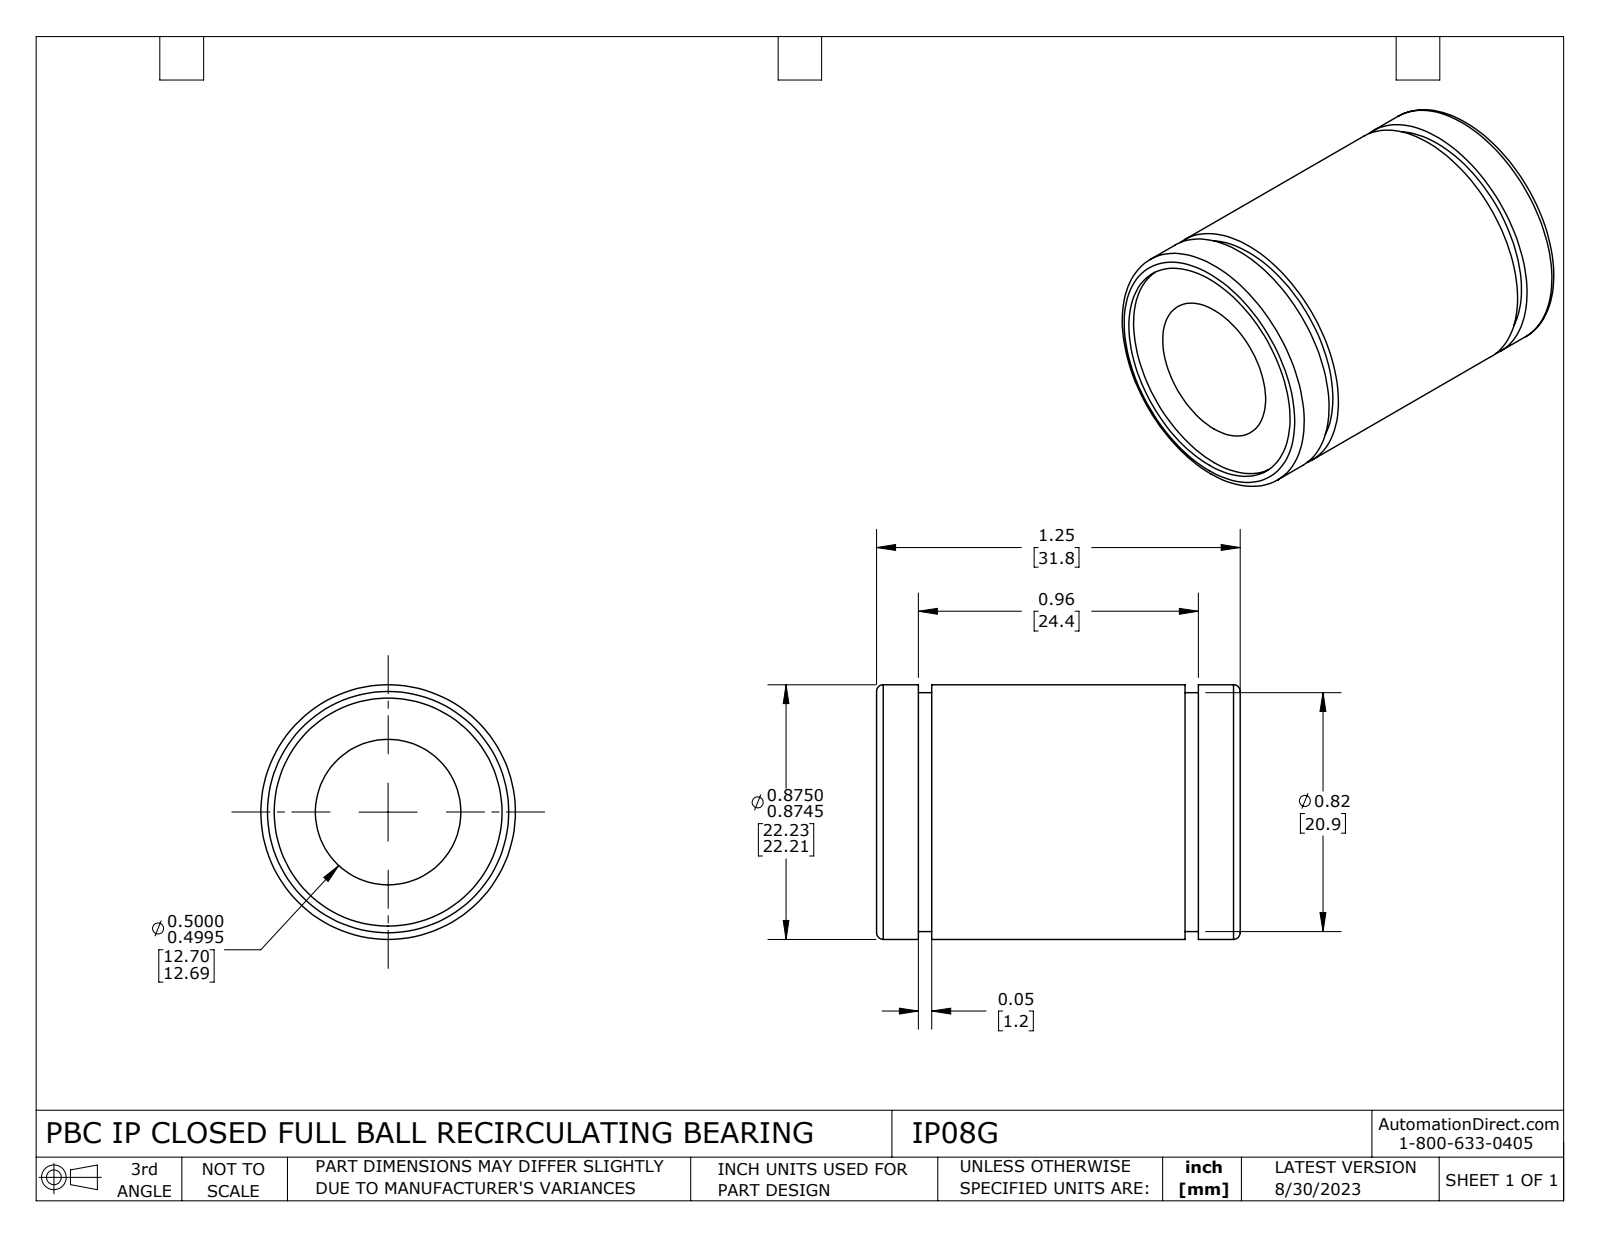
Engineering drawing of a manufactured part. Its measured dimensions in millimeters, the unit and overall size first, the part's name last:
Units: millimetres
Overall size (bounding box): 31.8 × 22.2 × 22.2
Round holes (diameter × count): ⌀12.7 ×1, ⌀19.9 ×1
Round bosses / shafts (diameter × count): ⌀22.2 ×1, ⌀20.9 ×1
Main face-to-face distances: 30.6, 3.1, 4.2, 26.3, 27.5, 23.3, 1.2, 0.6, 3.7, 4.8
Volume: 7 960 mm³ · Surface area: 4 173 mm²
Bodies: 1 solid, 28 faces (8 planar, 16 cylindrical, 4 other)
Part name (STEP PRODUCT): IP08G
STEP written by: SolidWorks 2021 (CONFIG_CONTROL_DESIGN)
